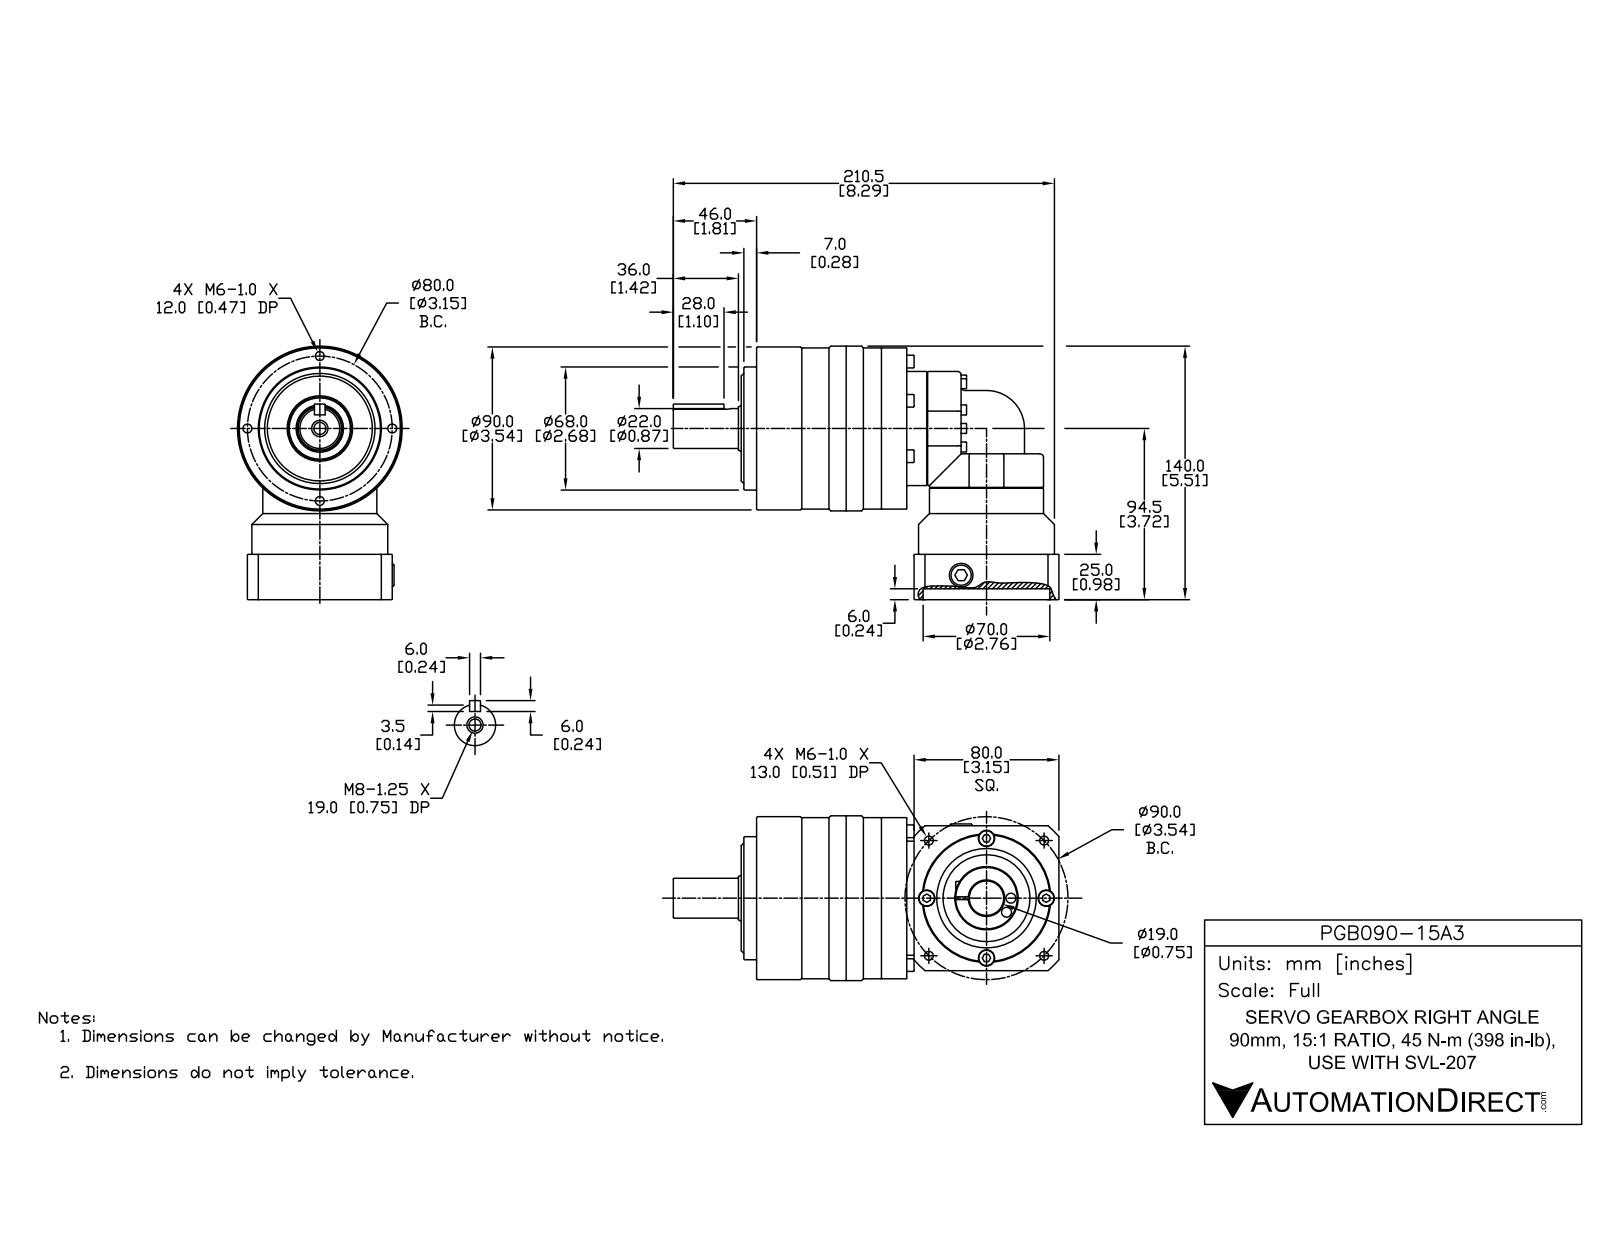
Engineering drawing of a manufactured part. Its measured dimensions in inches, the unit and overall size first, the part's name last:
Units: inches
Overall size (bounding box): 8.386 × 5.512 × 3.583
Round holes (diameter × count): ⌀0.194 ×8, ⌀0.177 ×7, ⌀0.354 ×4, ⌀0.217 ×2, ⌀0.128 ×1, ⌀0.262 ×1, ⌀0.413 ×1, ⌀0.748 ×1, ⌀1.89 ×1, ⌀2.165 ×1, ⌀2.756 ×1
Round bosses / shafts (diameter × count): ⌀0.217 ×9, ⌀0.276 ×7, ⌀0.157 ×7, ⌀0.335 ×4, ⌀2.48 ×2, ⌀2.362 ×2, ⌀3.583 ×1, ⌀3.543 ×1
Partial cylindrical surfaces — rounded edges, fillets, slot ends (radius × count): R0.079 ×6, R0.827 ×2, R0.118 ×1, R0.157 ×1, R2.067 ×1
Main face-to-face distances: 3.15, 0.748, 3.268, 0.984, 0.236, 0.157, 0.335, 3.602, 3.425, 3.76
Hole centre spacings: 1.254, 2.843, 0.615, 1.575, 1.75, 2.619, 3.089, 1.206
Volume: 59.64 in³ · Surface area: 144.1 in²
Bodies: 1 solid, 642 faces (258 planar, 167 cylindrical, 217 other)
Part name (STEP PRODUCT): PGB090-15A3
STEP written by: SolidWorks 2014 (AUTOMOTIVE_DESIGN)
